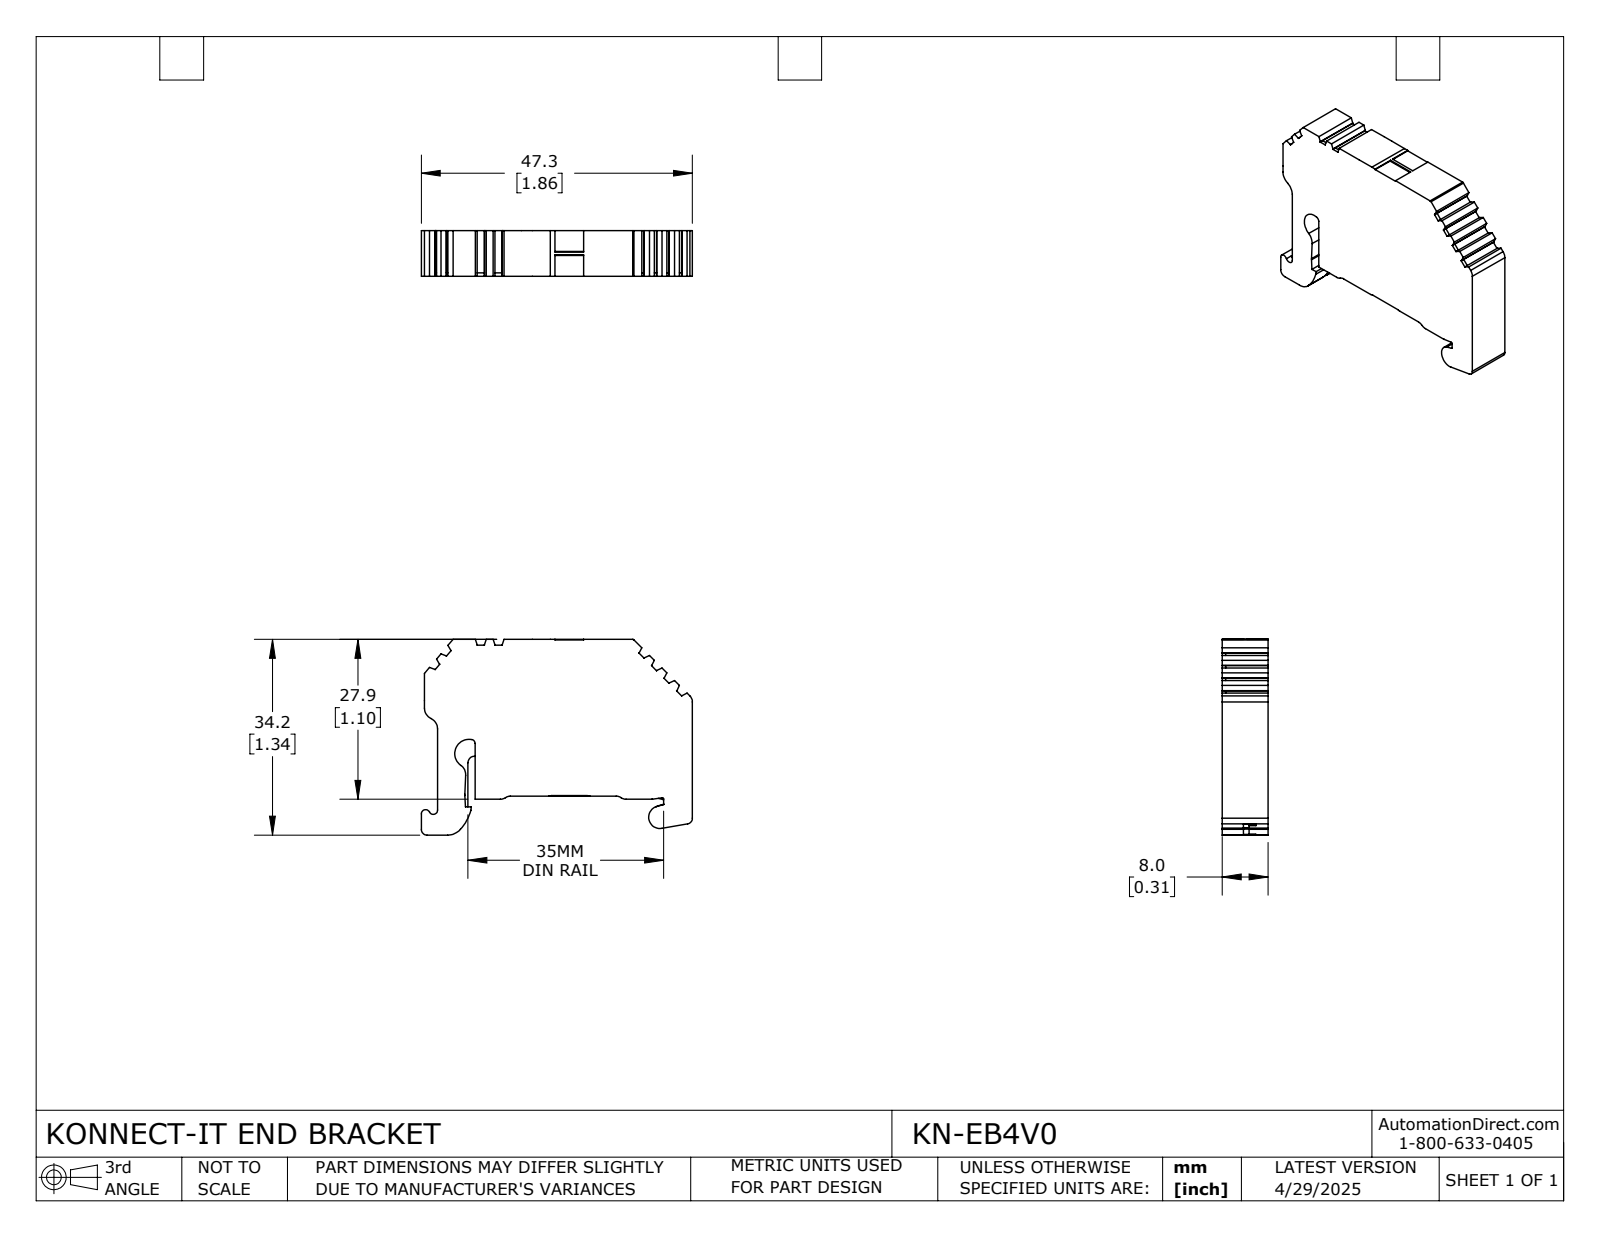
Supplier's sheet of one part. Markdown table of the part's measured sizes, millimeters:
| quantity | value |
| --- | --- |
| part name | KN-EB4V0 |
| STEP written by | SolidWorks 2024 (CONFIG_CONTROL_DESIGN) |
| units | millimeters |
| bodies | 1 solid, 259 faces (168 planar, 90 cylindrical, 1 other) |
| overall size | 47.34 × 34.16 × 8 |
| volume | 9 824 mm³ |
| surface area | 4 176 mm² |
| partial cylindrical surfaces (radius × count) | 0.5 × 17, 1.5 × 5, 2 × 4, 0.2 × 3, 0.3 × 3, 1 × 3, 0.4 × 2, 0.75 × 2 |
| main face-to-face distances | 8, 44.5, 27.36, 1.11, 27.26, 2.93, 6.55, 37.95, 0.54, 27.9 |
